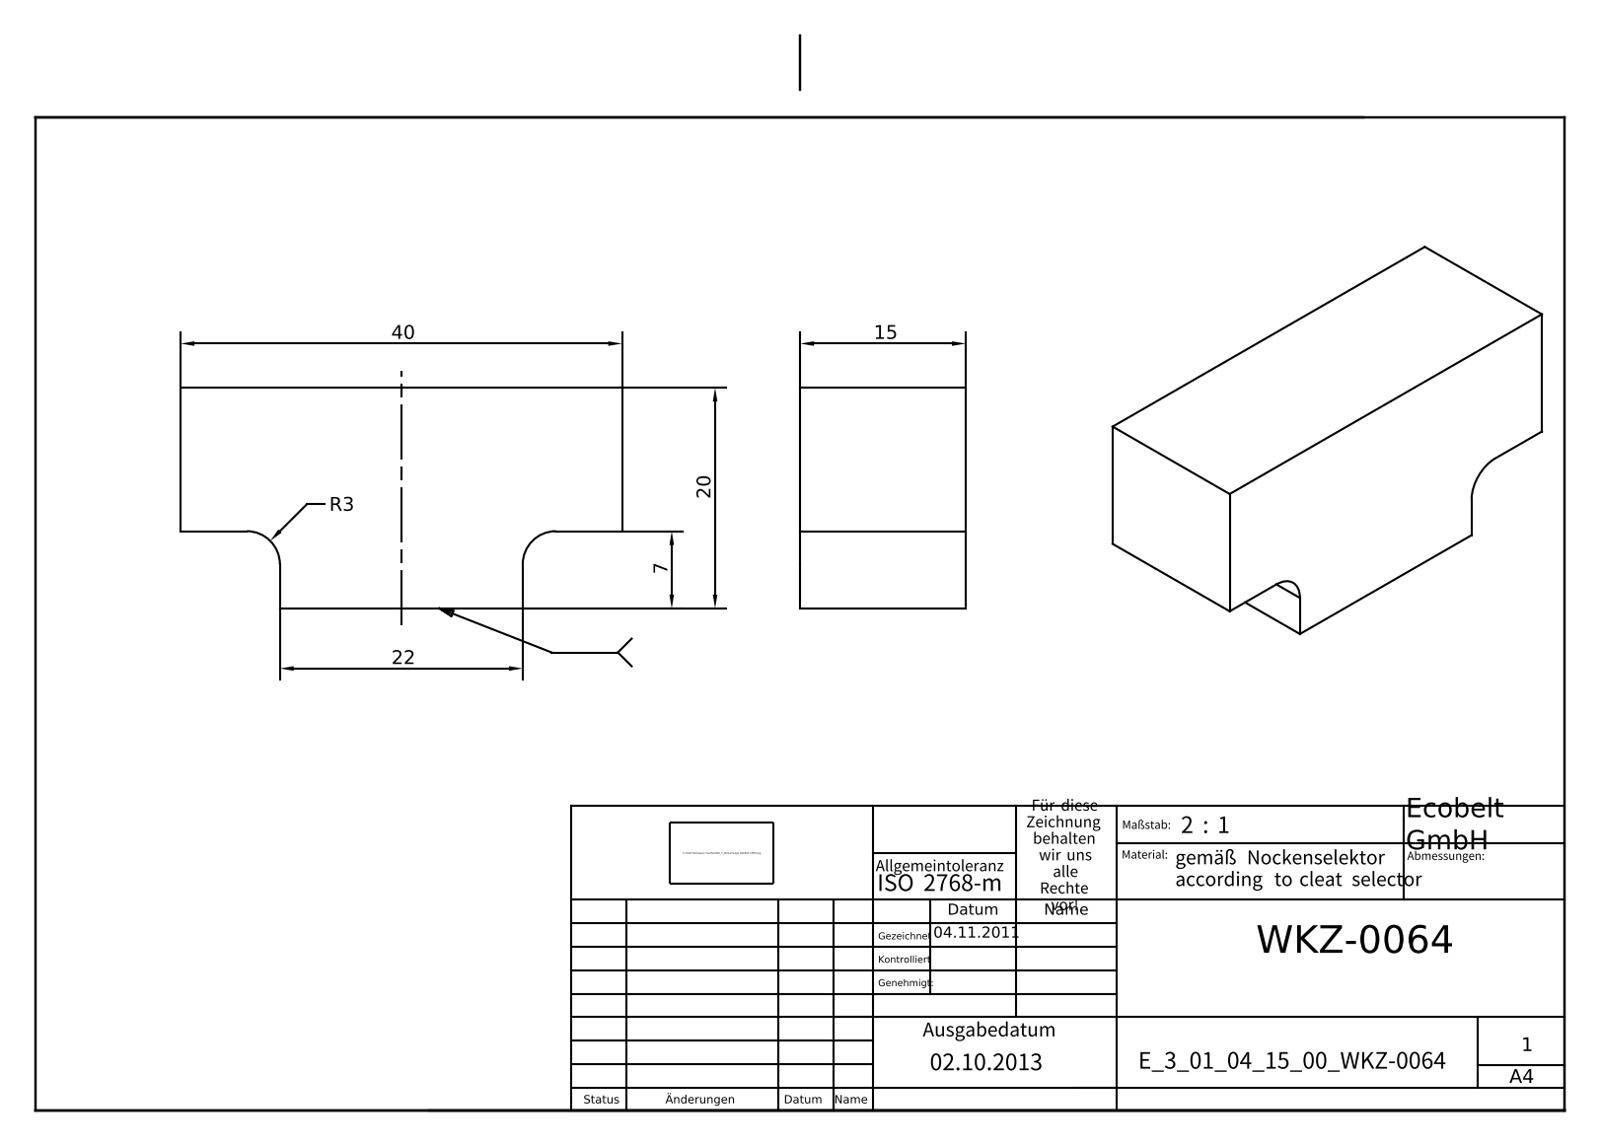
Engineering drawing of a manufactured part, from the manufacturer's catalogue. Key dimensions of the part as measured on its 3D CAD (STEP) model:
Part name (STEP PRODUCT): E_3_01_04_15_00_WKZ-0064
STEP written by: Autodesk Inventor 2025 (AUTOMOTIVE_DESIGN)
Units: millimetres
Bodies: 1 solid, 12 faces (10 planar, 2 cylindrical, 0 other)
Overall size (bounding box): 40 × 20 × 15
Volume: 10 168 mm³ · Surface area: 3 117 mm²
Partial cylindrical surfaces — rounded edges, fillets, slot ends (radius × count): R3 ×2
Main face-to-face distances: 15, 20, 40, 7, 13, 9, 31, 22
